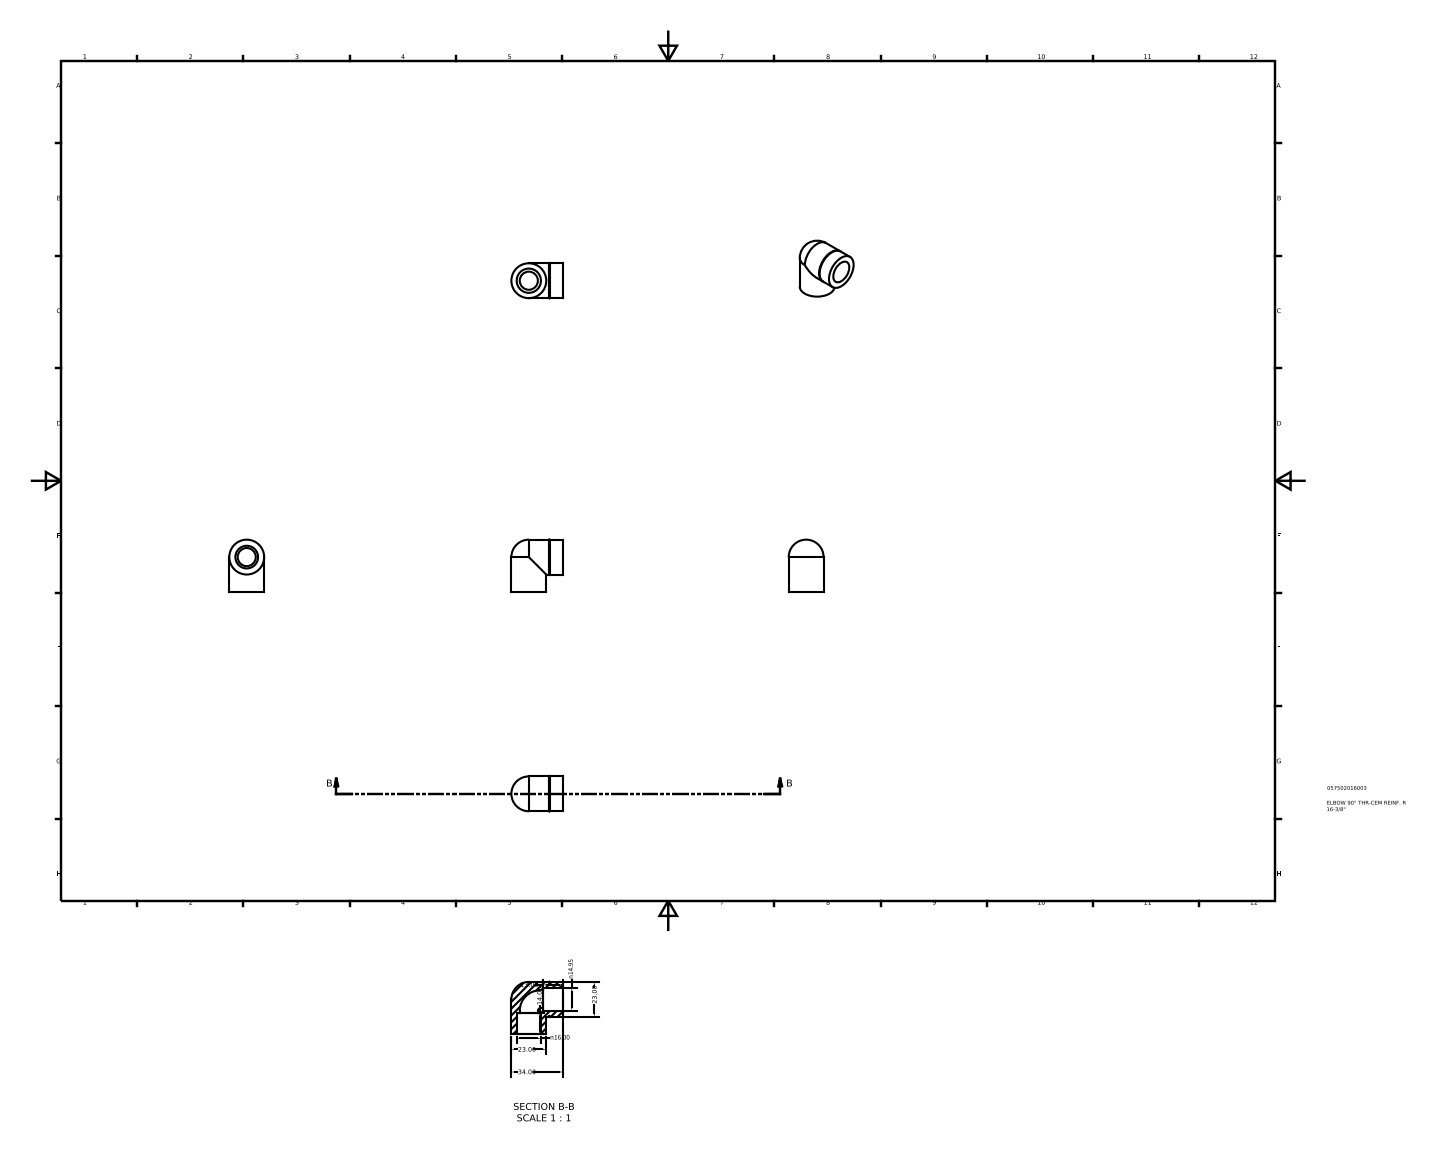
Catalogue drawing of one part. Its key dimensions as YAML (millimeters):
part_name: "057502016003"
step_written_by: "Autodesk Inventor 2015 (AUTOMOTIVE_DESIGN)"
units: millimeters
bodies: {solids: 1, faces: 15, planar: 4, cylindrical: 7, other: 4}
overall_size: [34.5, 34, 23]
volume: 11645
surface_area: 5712
round_holes:
  - {diameter: 11.96, count: 2}
  - {diameter: 14.95, count: 1}
  - {diameter: 16, count: 1}
round_bosses_or_shafts:
  - {diameter: 23, count: 2}
face_to_face_distances: [14, 13]
